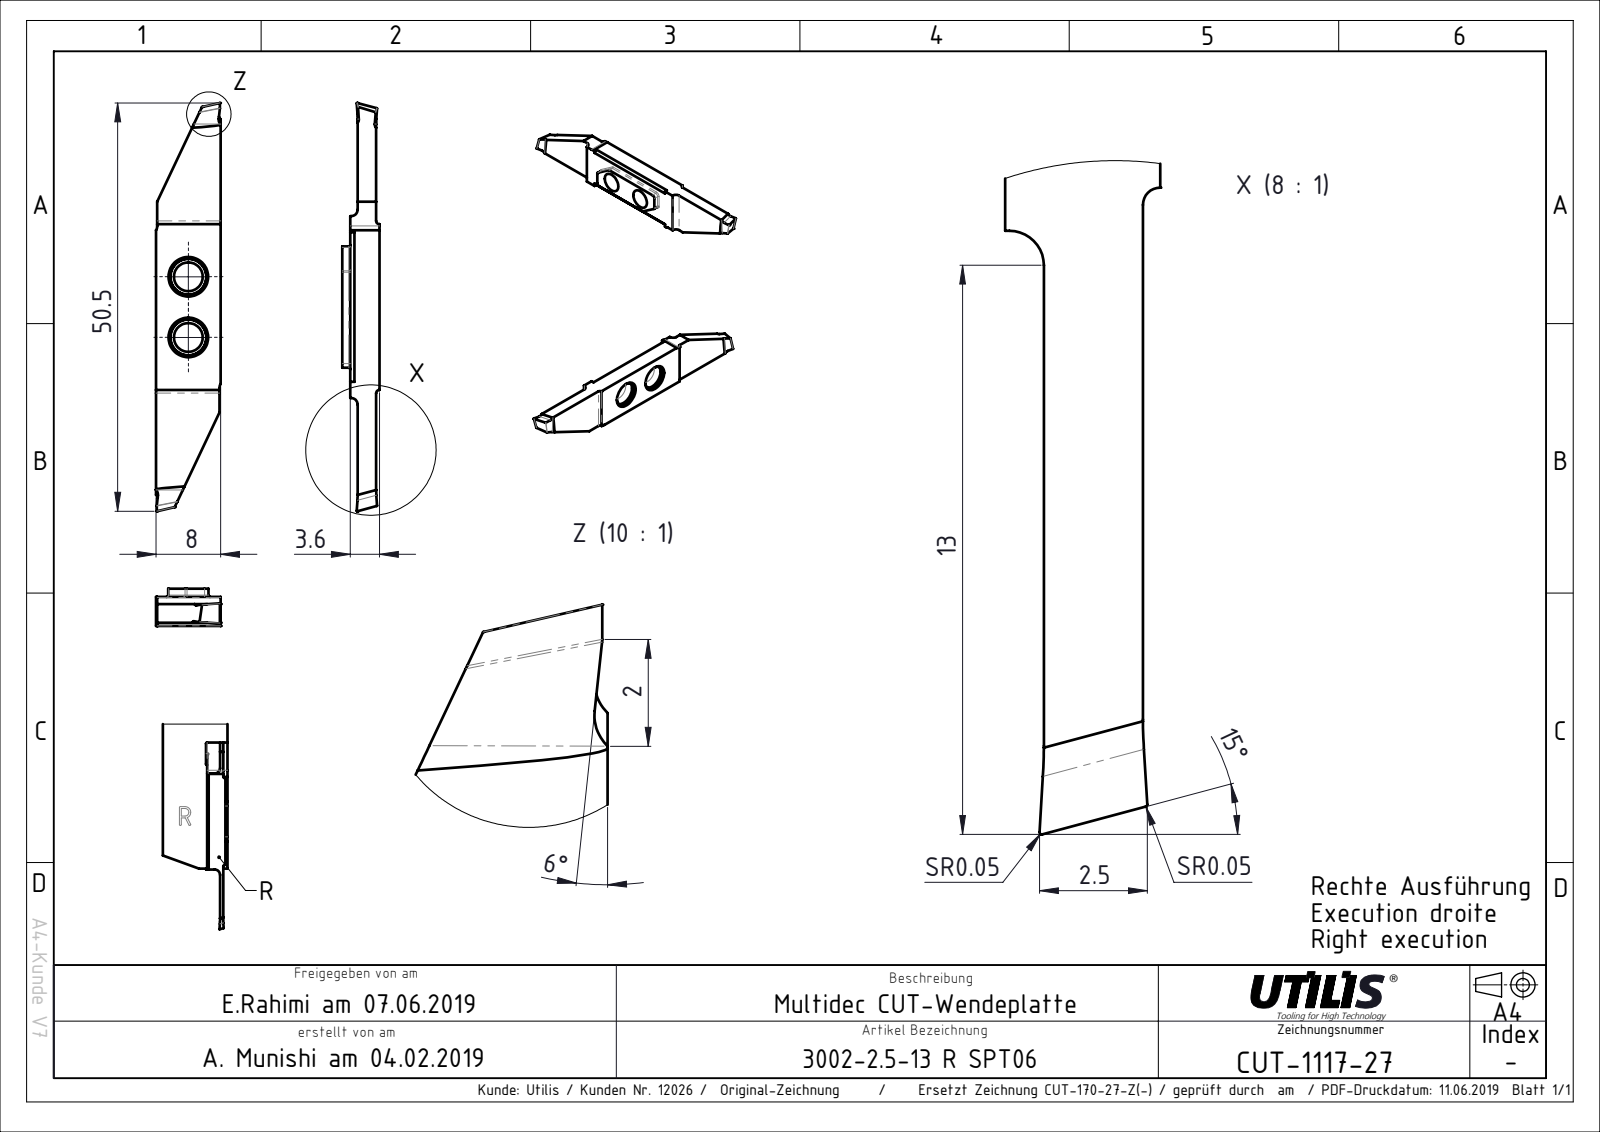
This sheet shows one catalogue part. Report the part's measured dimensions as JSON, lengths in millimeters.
{"part_name": "CUT-1117; ASME Y14.5", "step_written_by": "FormatWorks Professional (AP242_MANAGED_MODEL_BASED_3D_ENGINEERING_MIM_LF)", "units": "millimeters", "bodies": {"solids": 1, "faces": 44, "planar": 28, "cylindrical": 16, "other": 0}, "overall_size": [50.5, 8, 3.6], "volume_mm3": 907, "surface_area_mm2": 1002, "round_holes": [[3.55, 2]], "partial_cylinders_radius": [[0.4, 2], [0.8, 2], [1, 2]], "face_to_face_distances": [0.4, 3.2, 3.6, 0.9, 2.3, 2.7, 8, 18.09, 7.85, 7.7], "hole_center_spacings": [7.5]}
